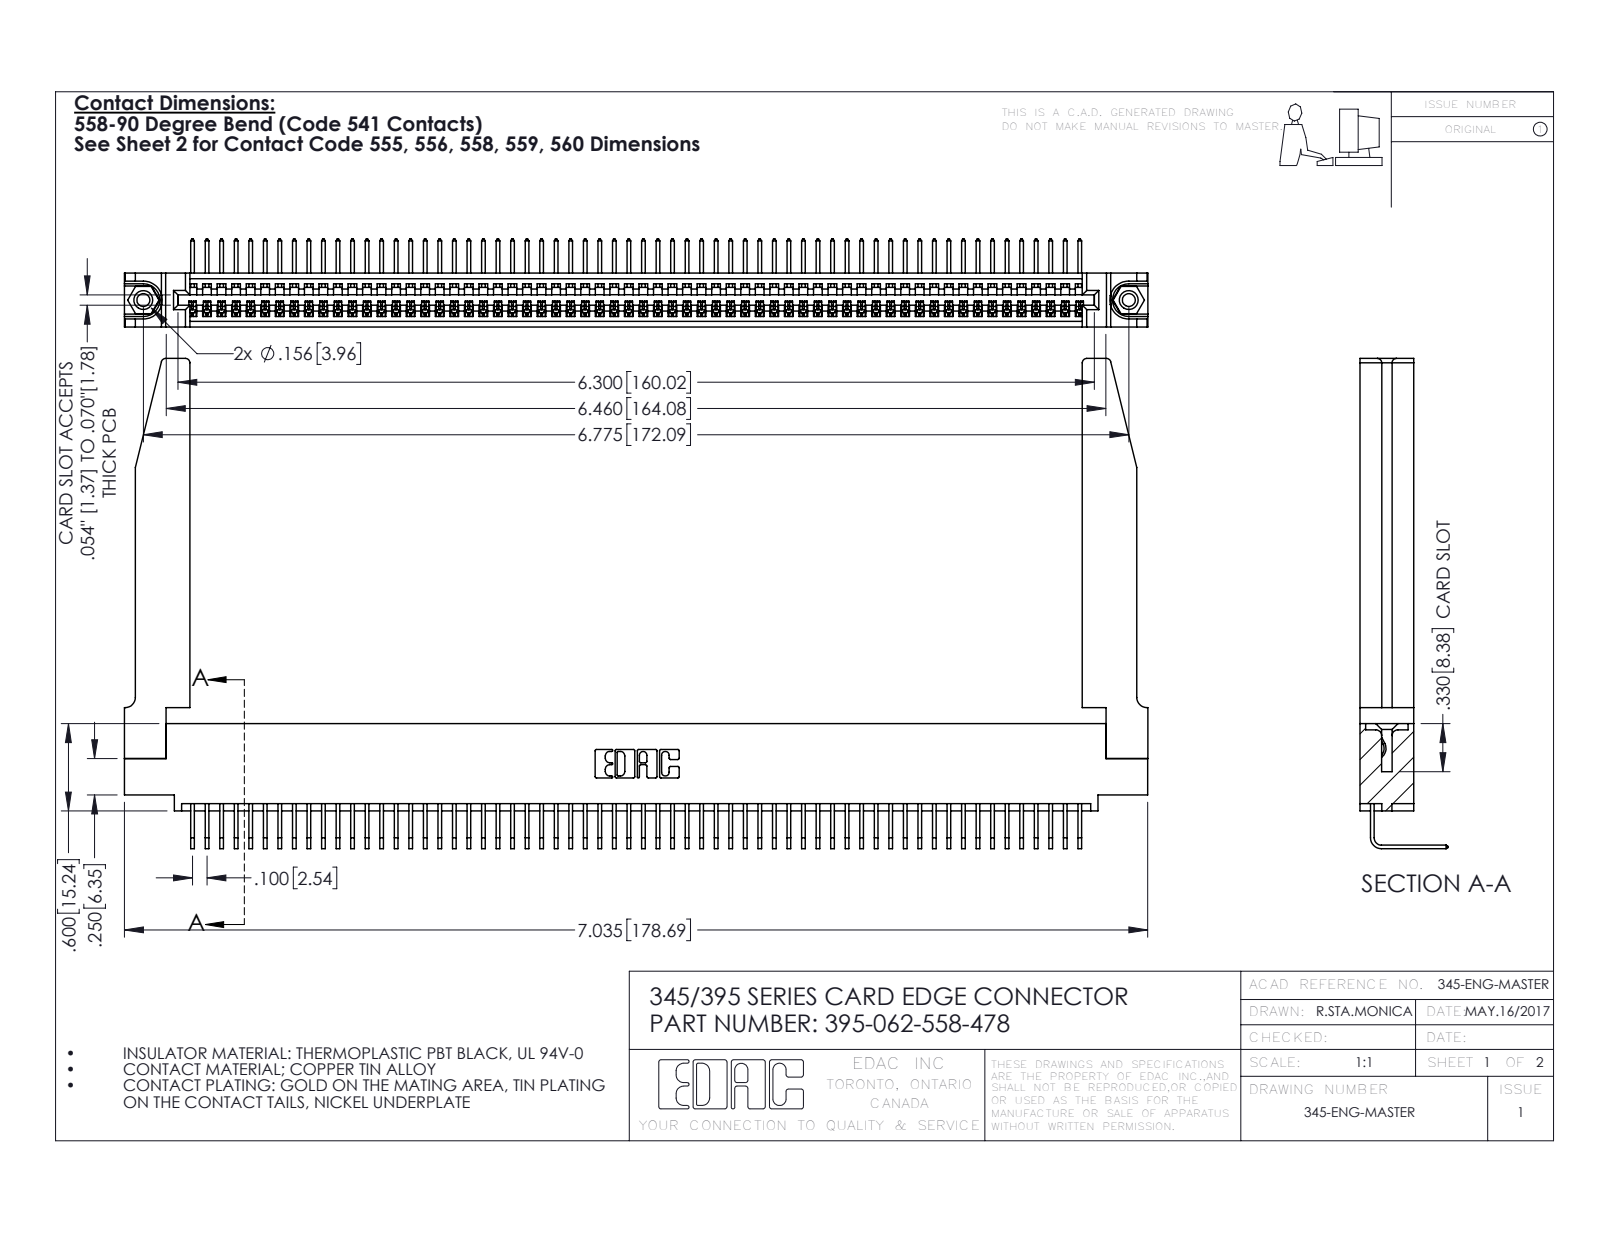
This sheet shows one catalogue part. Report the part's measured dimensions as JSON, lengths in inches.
{"part_name": "345-220-078_345-220-078; 345-292-001_558 Tail - 2; 395-062-558-478; 345-250-001_345-250-001-102 (+1 more)", "step_written_by": "SolidWorks 2016 (CONFIG_CONTROL_DESIGN)", "units": "inches", "bodies": {"solids": 67, "faces": 4084, "planar": 2830, "cylindrical": 1202, "other": 52}, "overall_size": [7.036, 3.369, 0.605], "volume_in3": 1.528, "surface_area_in2": 48.62, "round_holes": [[0.089, 2], [0.125, 2], [0.156, 2], [0.064, 1]], "round_bosses_or_shafts": [[0.155, 2]], "partial_cylinders_radius": [[0.006, 124], [0.01, 22], [0.03, 8], [0.007, 6], [0.031, 6], [0.026, 3], [0.031, 2], [0.04, 2]], "face_to_face_distances": [0.072, 0.37, 0.298, 0.098, 0.272, 0.025, 0.2, 0.225, 0.148, 0.15], "hole_center_spacings": [0.27, 6.539, 6.775]}
